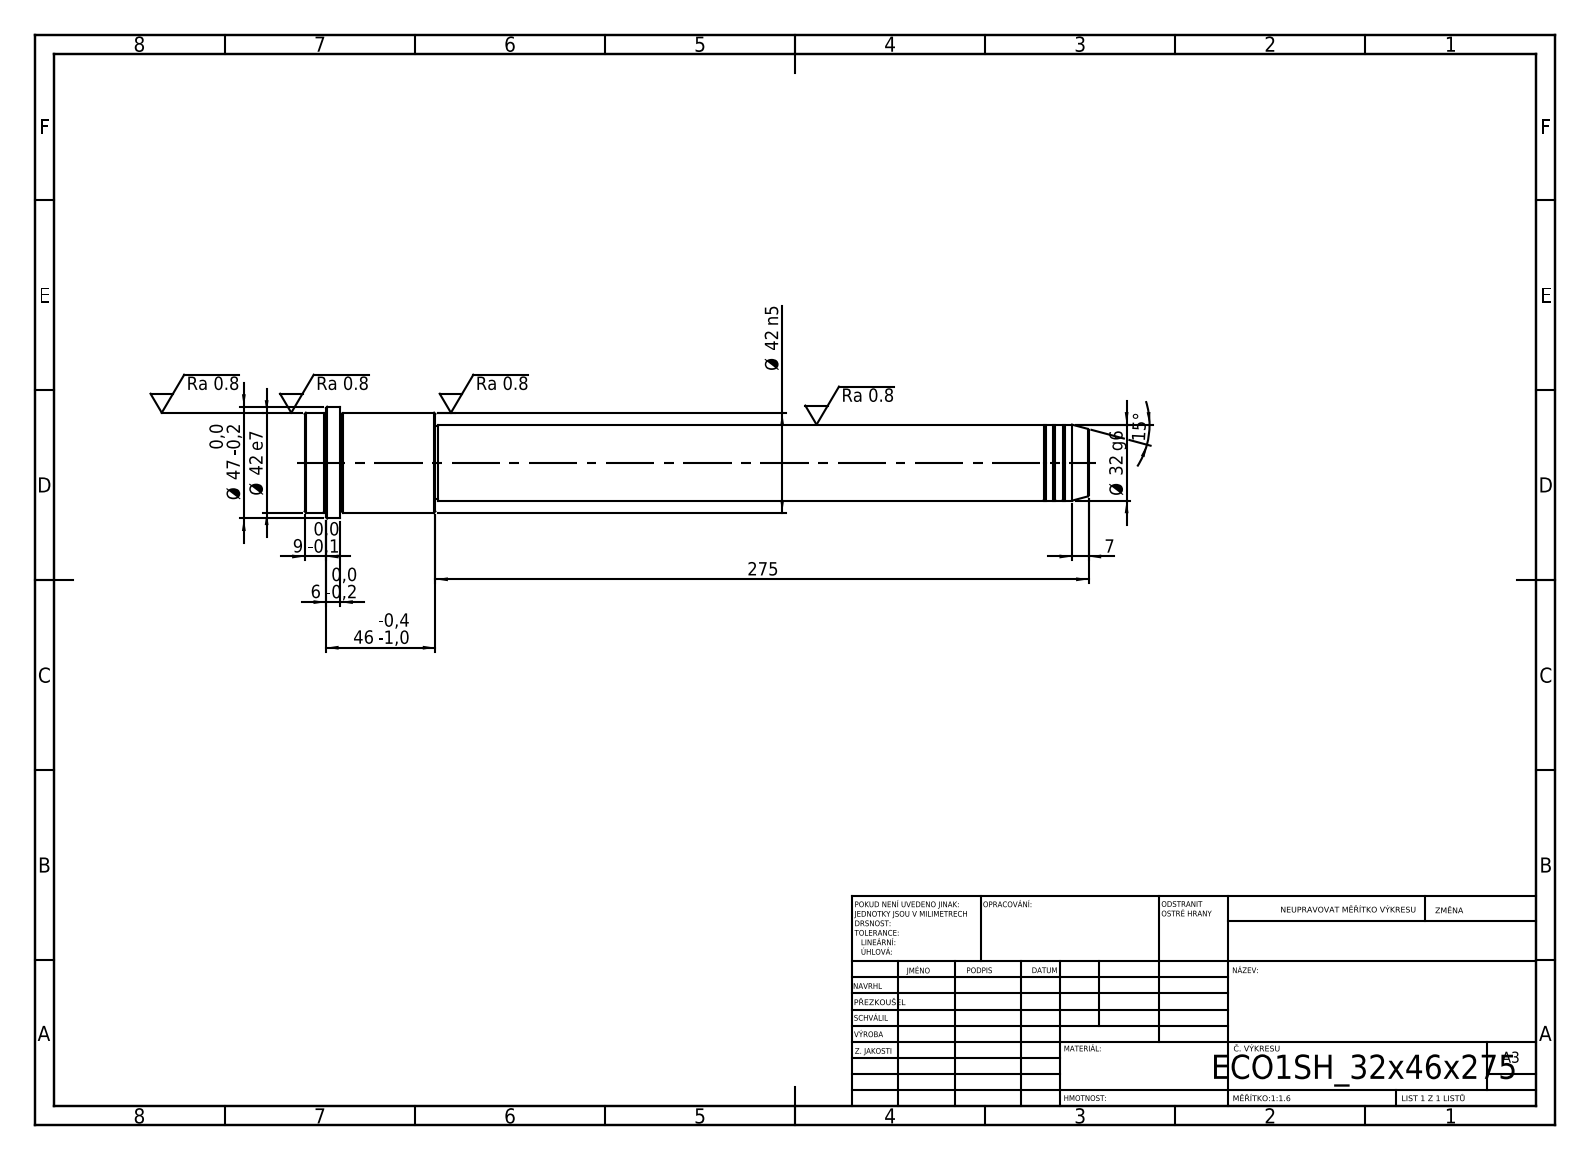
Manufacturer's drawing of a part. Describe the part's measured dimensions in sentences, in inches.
Its 3-D file was written by "SolidWorks 2019 (CONFIG_CONTROL_DESIGN)". It is 1 solid with 52 faces: 6 planar, 16 cylindrical and 30 other. Overall it measures 12.992 by 1.85 by 1.85 inches. Its volume is 18.22 cubic inches and its surface area 59.74 square inches. Round bosses or shafts: 1 of diameter 1.85, 1 of diameter 1.654, 1 of diameter 1.26, 1 of diameter 1.22. The main face-to-face distances are 12.992, 10.827, 2.165, 12.402, 1.575, 0.591, 12.638, 1.811, 0.236, 0.354.
